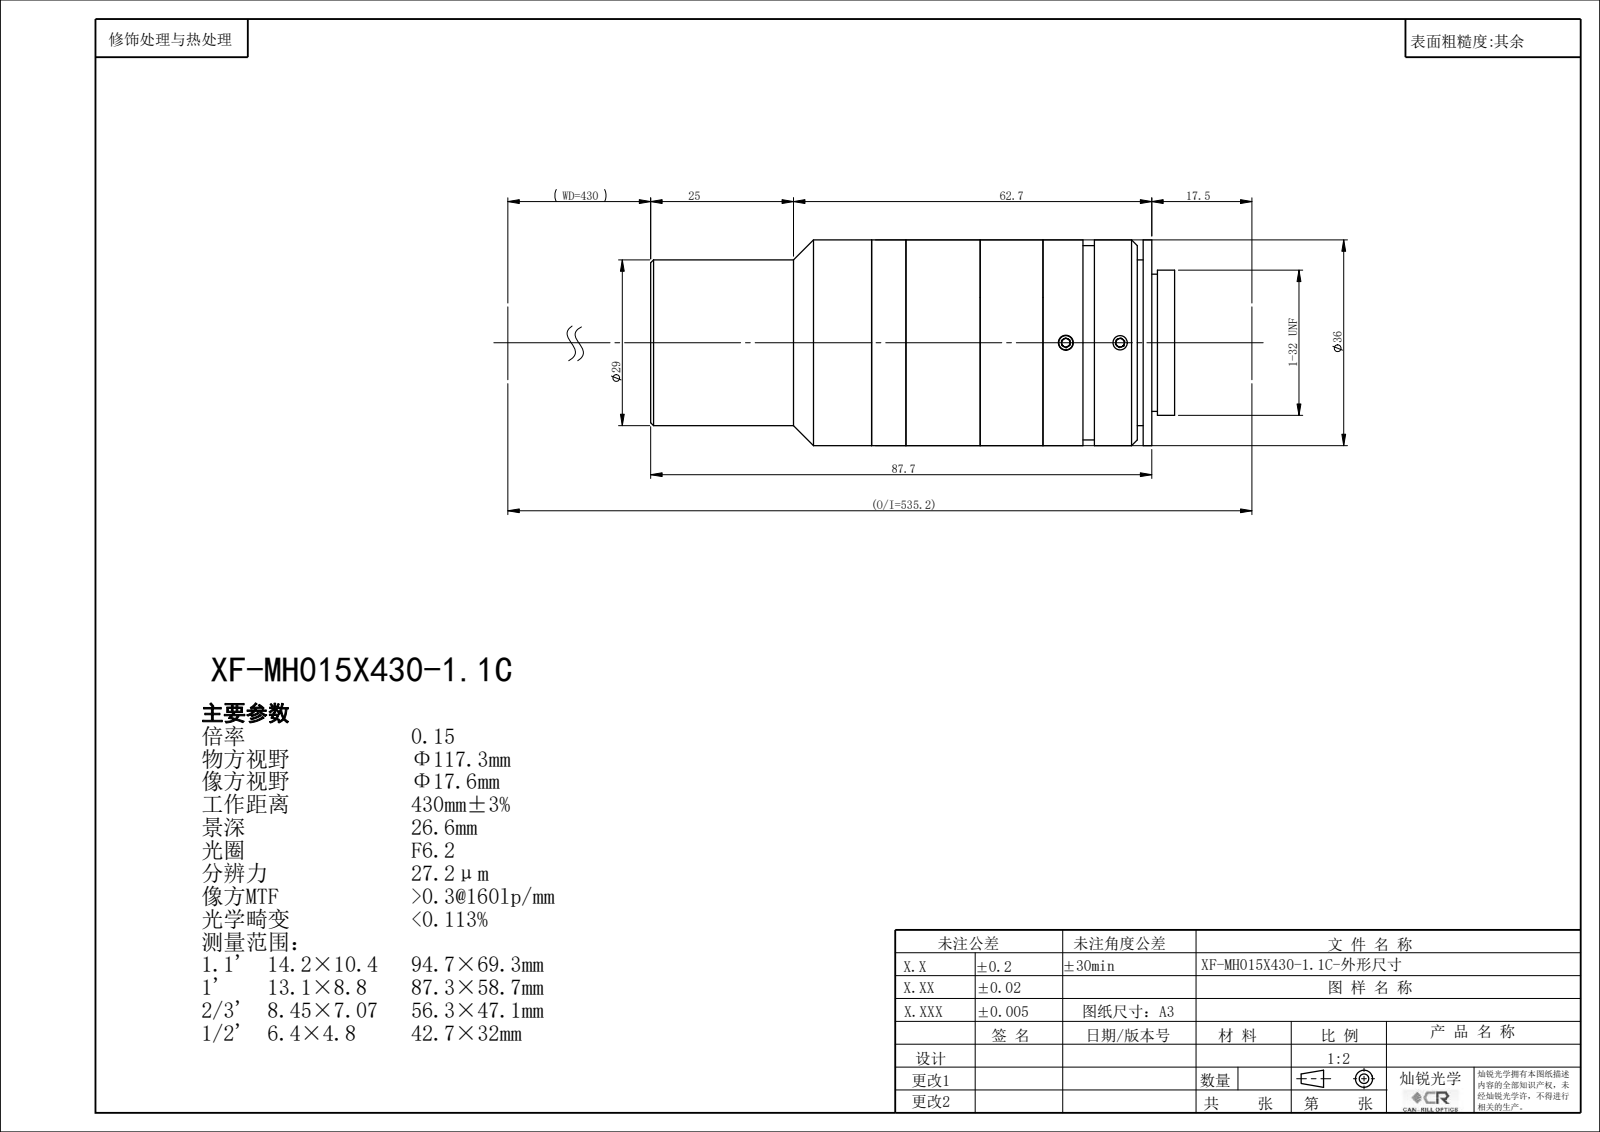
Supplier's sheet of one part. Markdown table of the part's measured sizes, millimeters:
| quantity | value |
| --- | --- |
| part name | XF-MH015X430-1.1C |
| STEP written by | SolidWorks 2022 (CONFIG_CONTROL_DESIGN) |
| units | millimeters |
| bodies | 0 solids, 141 faces (71 planar, 42 cylindrical, 28 other) |
| overall size | 91.72 × 36 × 36 |
| round holes (diameter × count) | 2.5 × 3, 20 × 1, 22.4 × 1, 24 × 1, 24.9 × 1, 26 × 1, 26.4 × 1 |
| round bosses / shafts (diameter × count) | 36 × 1, 34 × 1, 29 × 1, 25.4 × 1 |
| main face-to-face distances | 19.04, 1.5, 17.54, 11, 28.54, 30.04, 6, 17, 11.54, 13.04 |
